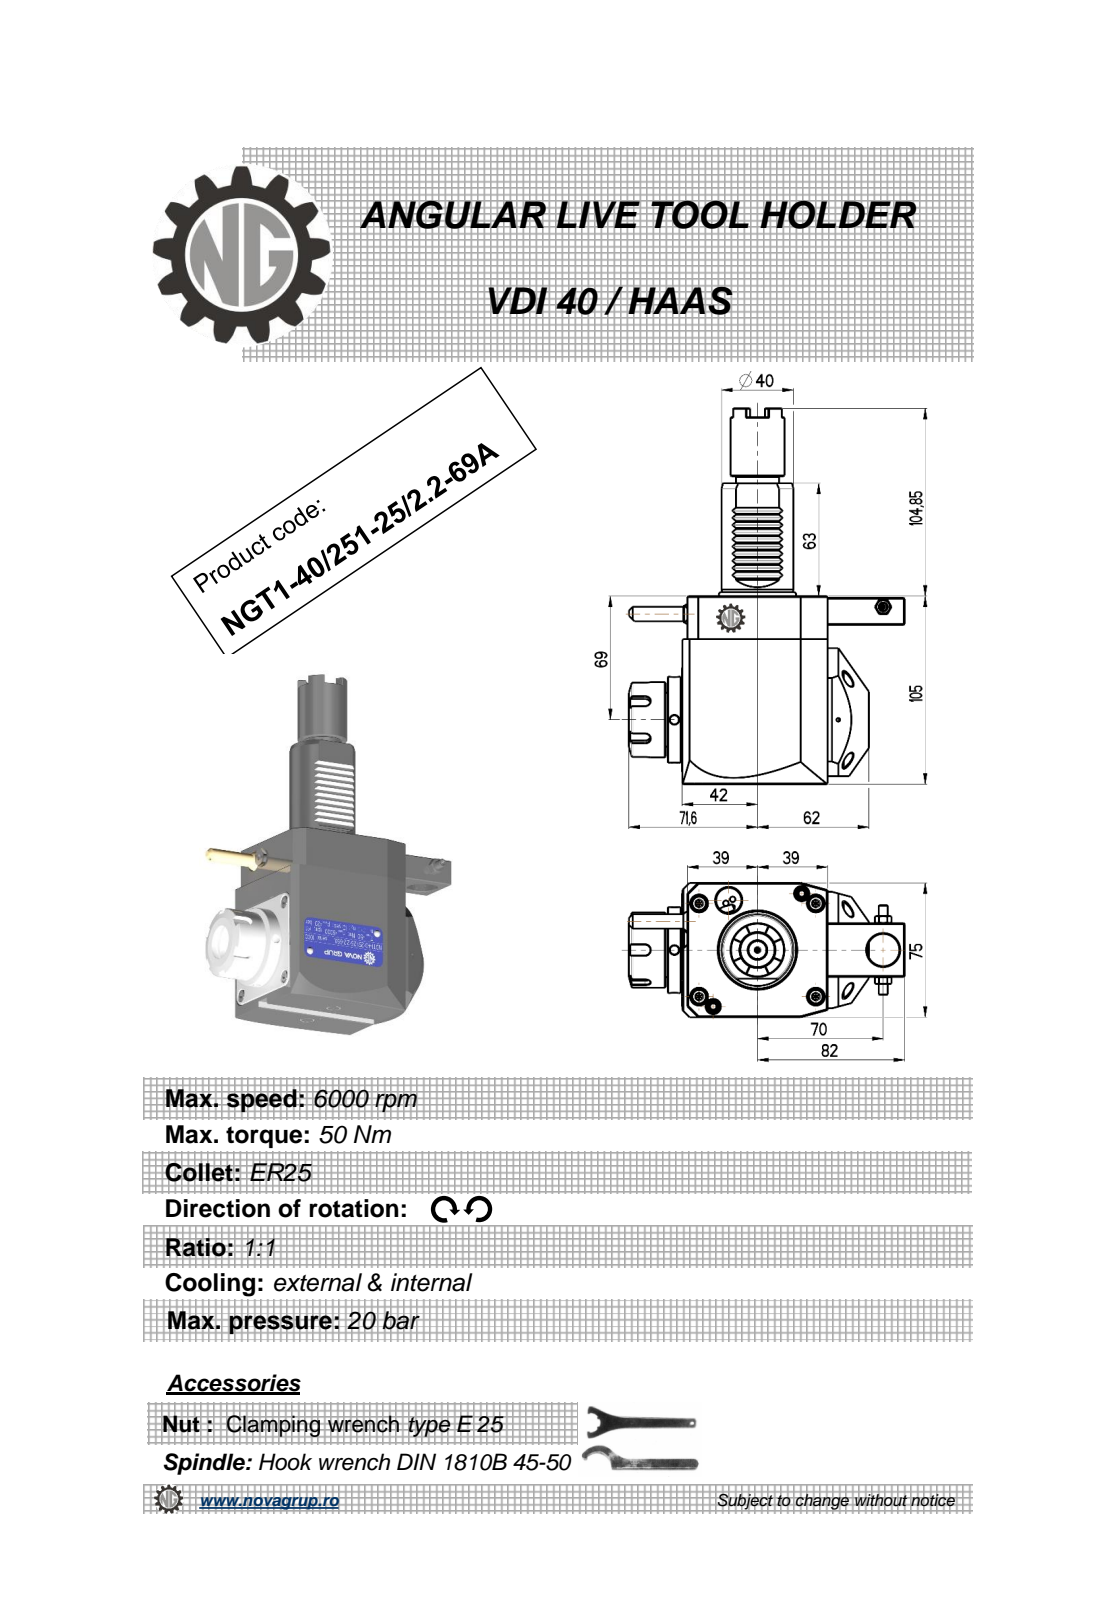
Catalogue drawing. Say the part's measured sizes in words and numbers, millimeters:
The part is named "NGT1_40_251_25_2_2_69A". Its 3-D file was written by "PRO/ENGINEER BY PARAMETRIC TECHNOLOGY CORPORATION, 2010280 (CONFIG_CONTROL_DESIGN)". It is 1 solid with 476 faces: 223 planar, 94 cylindrical and 159 other. Overall it measures 209.85 by 153.6 by 76.6 millimeters. Its volume is 842 565 cubic millimeters and its surface area 72 614 square millimeters. Round holes: 3 of diameter 5, 1 of diameter 3, 1 of diameter 4.2, 1 of diameter 9.5, 1 of diameter 18, 1 of diameter 20.3. Round bosses or shafts: 1 of diameter 48, 1 of diameter 42, 1 of diameter 40, 1 of diameter 37.5, 1 of diameter 33, 1 of diameter 30, 1 of diameter 24, 1 of diameter 10. Partial cylindrical surfaces (rounded edges, fillets, slot ends): 12 of radius 0.26, 10 of radius 0.3, 6 of radius 0.2, 5 of radius 3, 1 of radius 0.5, 1 of radius 9.75, 1 of radius 40. The main face-to-face distances are 75, 105, 81, 104, 89, 80.8, 1, 101, 3, 2.8. The hole center spacings are 16.19, 61.13, 61.5, 116.25, 132.22.
